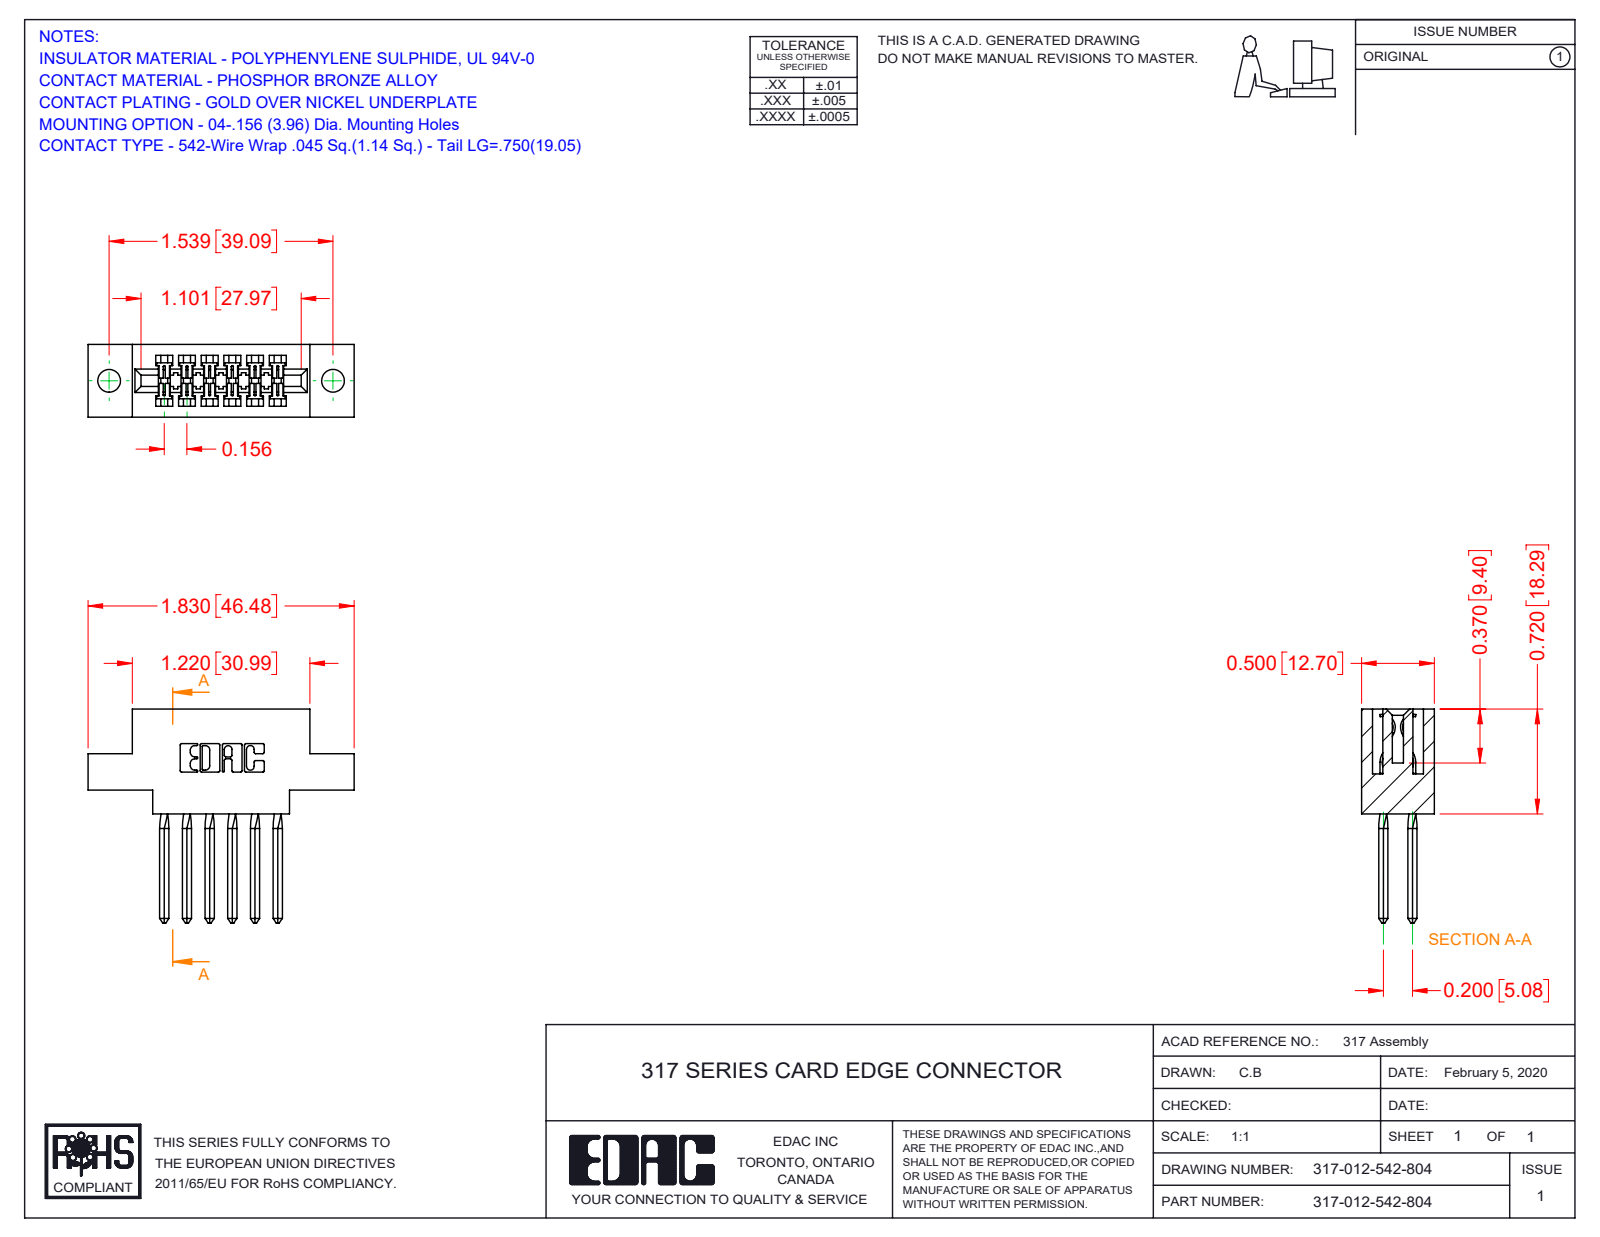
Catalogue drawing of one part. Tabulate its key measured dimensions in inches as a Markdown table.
| quantity | value |
| --- | --- |
| part name | 317-012-542-804; 317 Part_.156 Dia - TH; 317-290-003_542 |
| STEP written by | SolidWorks 2016 (CONFIG_CONTROL_DESIGN) |
| units | inches |
| bodies | 13 solids, 786 faces (610 planar, 128 cylindrical, 48 other) |
| overall size | 1.83 × 1.47 × 0.5 |
| volume | 0.39 in³ |
| surface area | 11.69 in² |
| round holes (diameter × count) | 0.156 × 2 |
| partial cylindrical surfaces (radius × count) | 0.006 × 24, 0.01 × 22, 0.007 × 6, 0.031 × 6, 0.026 × 3, 0.074 × 2, 0.089 × 2, 0.1 × 2 |
| main face-to-face distances | 0.5, 0.11, 0.075, 0.425, 0.22, 0.065, 0.116, 0.156, 0.045, 0.163 |
| hole center spacings | 1.539 |
